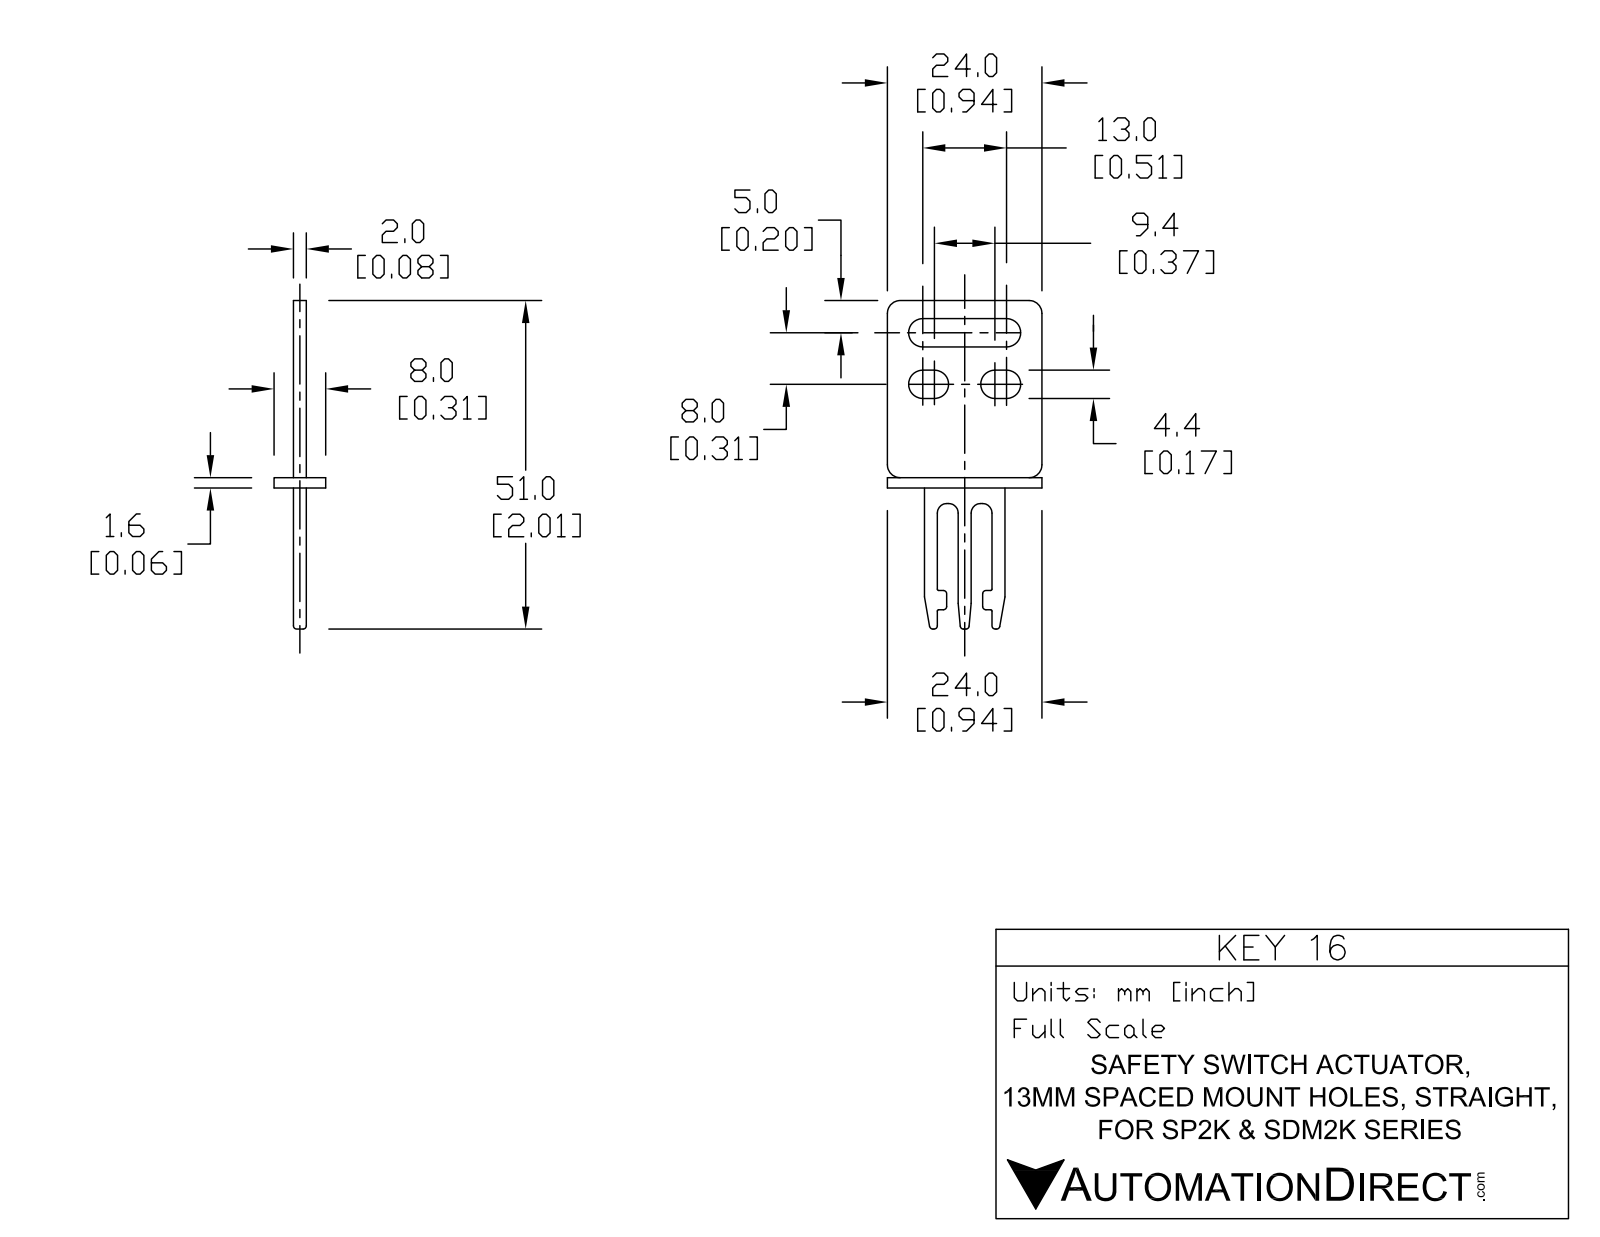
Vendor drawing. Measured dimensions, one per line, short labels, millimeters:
name: KEY16
written by: SolidWorks 2019 (CONFIG_CONTROL_DESIGN)
unit: mm
bodies: 2 solids, 165 faces (58 planar, 79 cylindrical, 28 other)
size: 51 × 24 × 8
volume: 1 670 mm³; area: 2 450 mm²
rounds: 42× R0.5, 8× R1, 6× R2.2, 4× R0.2, 4× R1.5
face distances: 2, 1.6, 3, 5, 24, 5.3, 8, 5.7, 18.3, 2.1
